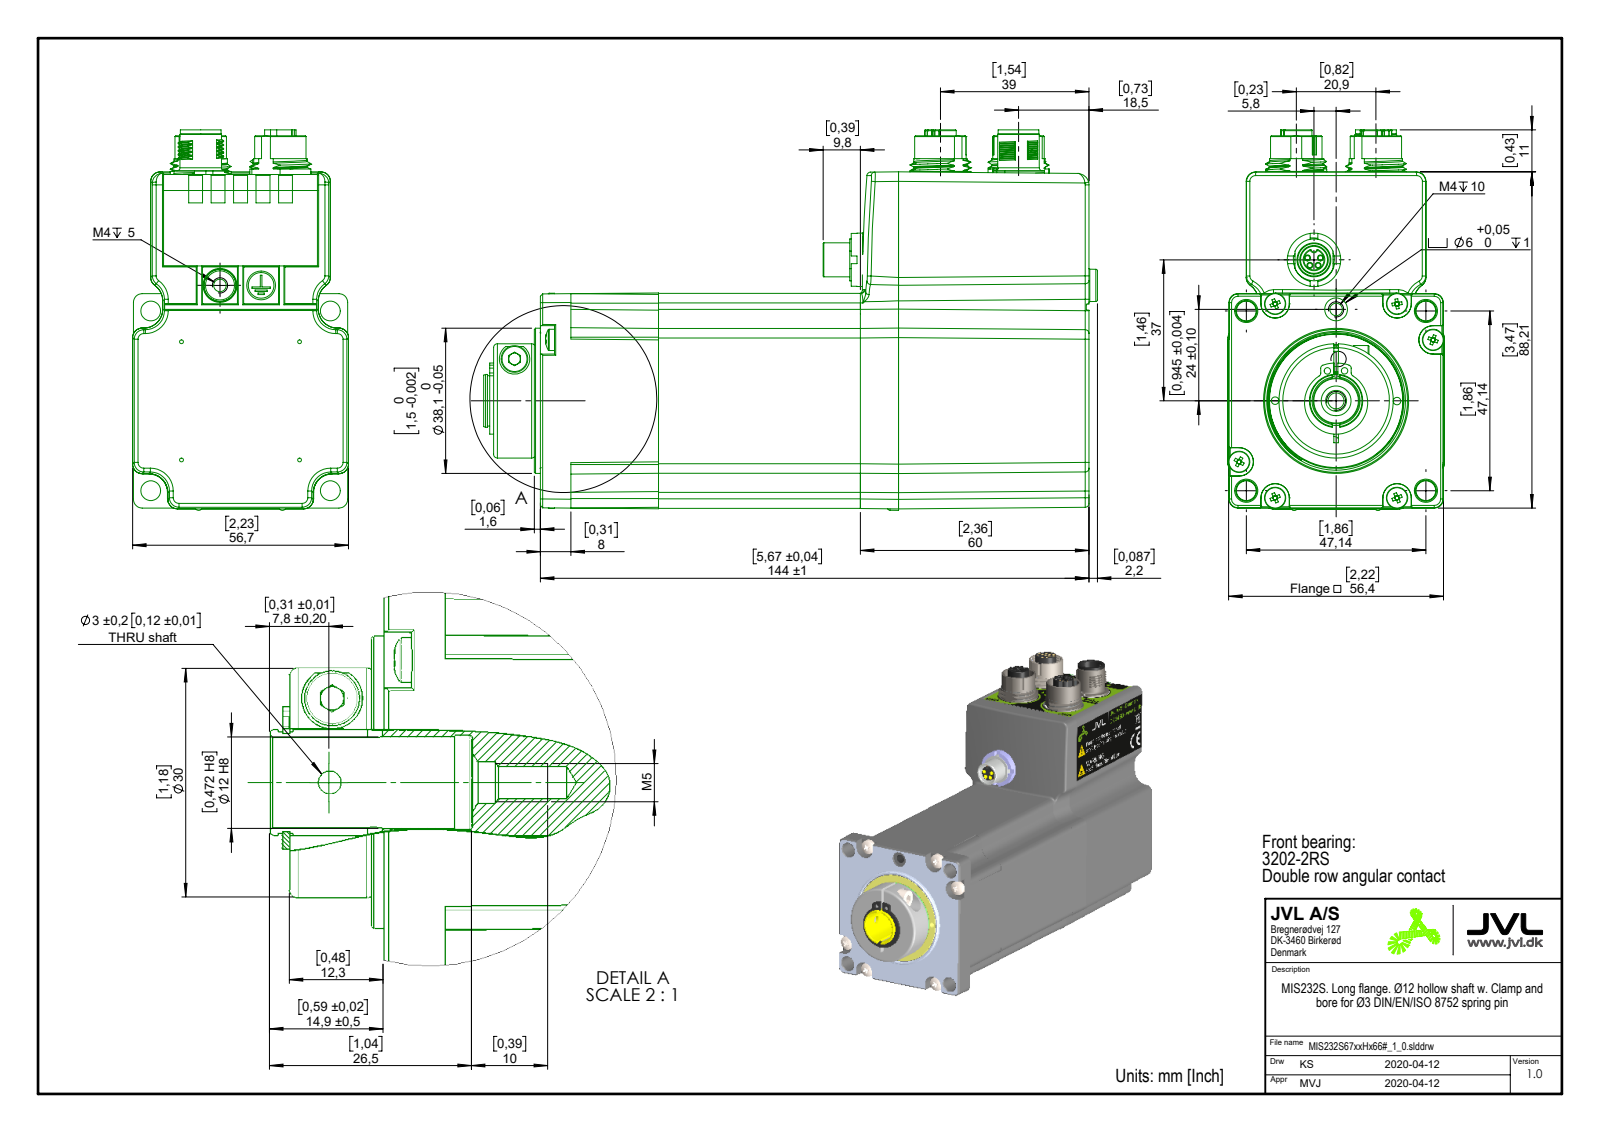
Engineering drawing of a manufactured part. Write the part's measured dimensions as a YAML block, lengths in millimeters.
part_name: "MIS232S67xxHx66#_1_0"
step_written_by: "SolidWorks 2018 (AUTOMOTIVE_DESIGN)"
units: millimeters
bodies: {solids: 4, faces: 2254, planar: 966, cylindrical: 581, other: 707}
overall_size: [161.1, 99.83, 56.67]
volume: 506686
surface_area: 62056
round_holes:
  - {diameter: 1, count: 31}
  - {diameter: 3.3, count: 6}
  - {diameter: 1.2, count: 4}
  - {diameter: 2, count: 4}
  - {diameter: 12.2, count: 3}
  - {diameter: 1.7, count: 2}
  - {diameter: 11.13, count: 2}
  - {diameter: 3, count: 1}
  - {diameter: 4, count: 1}
  - {diameter: 4.2, count: 1}
  - {diameter: 4.5, count: 1}
  - {diameter: 5.5, count: 1}
round_bosses_or_shafts:
  - {diameter: 5.6, count: 6}
  - {diameter: 3, count: 6}
  - {diameter: 1, count: 5}
  - {diameter: 1.6, count: 4}
  - {diameter: 0.8, count: 4}
  - {diameter: 13.5, count: 3}
  - {diameter: 16, count: 2}
  - {diameter: 14, count: 2}
partial_cylinders:
  - {radius: 0.2, count: 54}
  - {radius: 2.5, count: 29}
  - {radius: 0.1, count: 20}
  - {radius: 0.3, count: 16}
  - {radius: 1, count: 15}
  - {radius: 5, count: 14}
  - {radius: 0.8, count: 13}
  - {radius: 0.85, count: 4}
face_to_face_distances: [56.4, 57.23, 4.75, 52.48, 144, 88.68, 51.92, 0.56, 0.5, 4]
hole_center_spacings: [3.54, 1.63, 2.5, 3.25, 1.85, 4.94, 1.64, 2.83]
